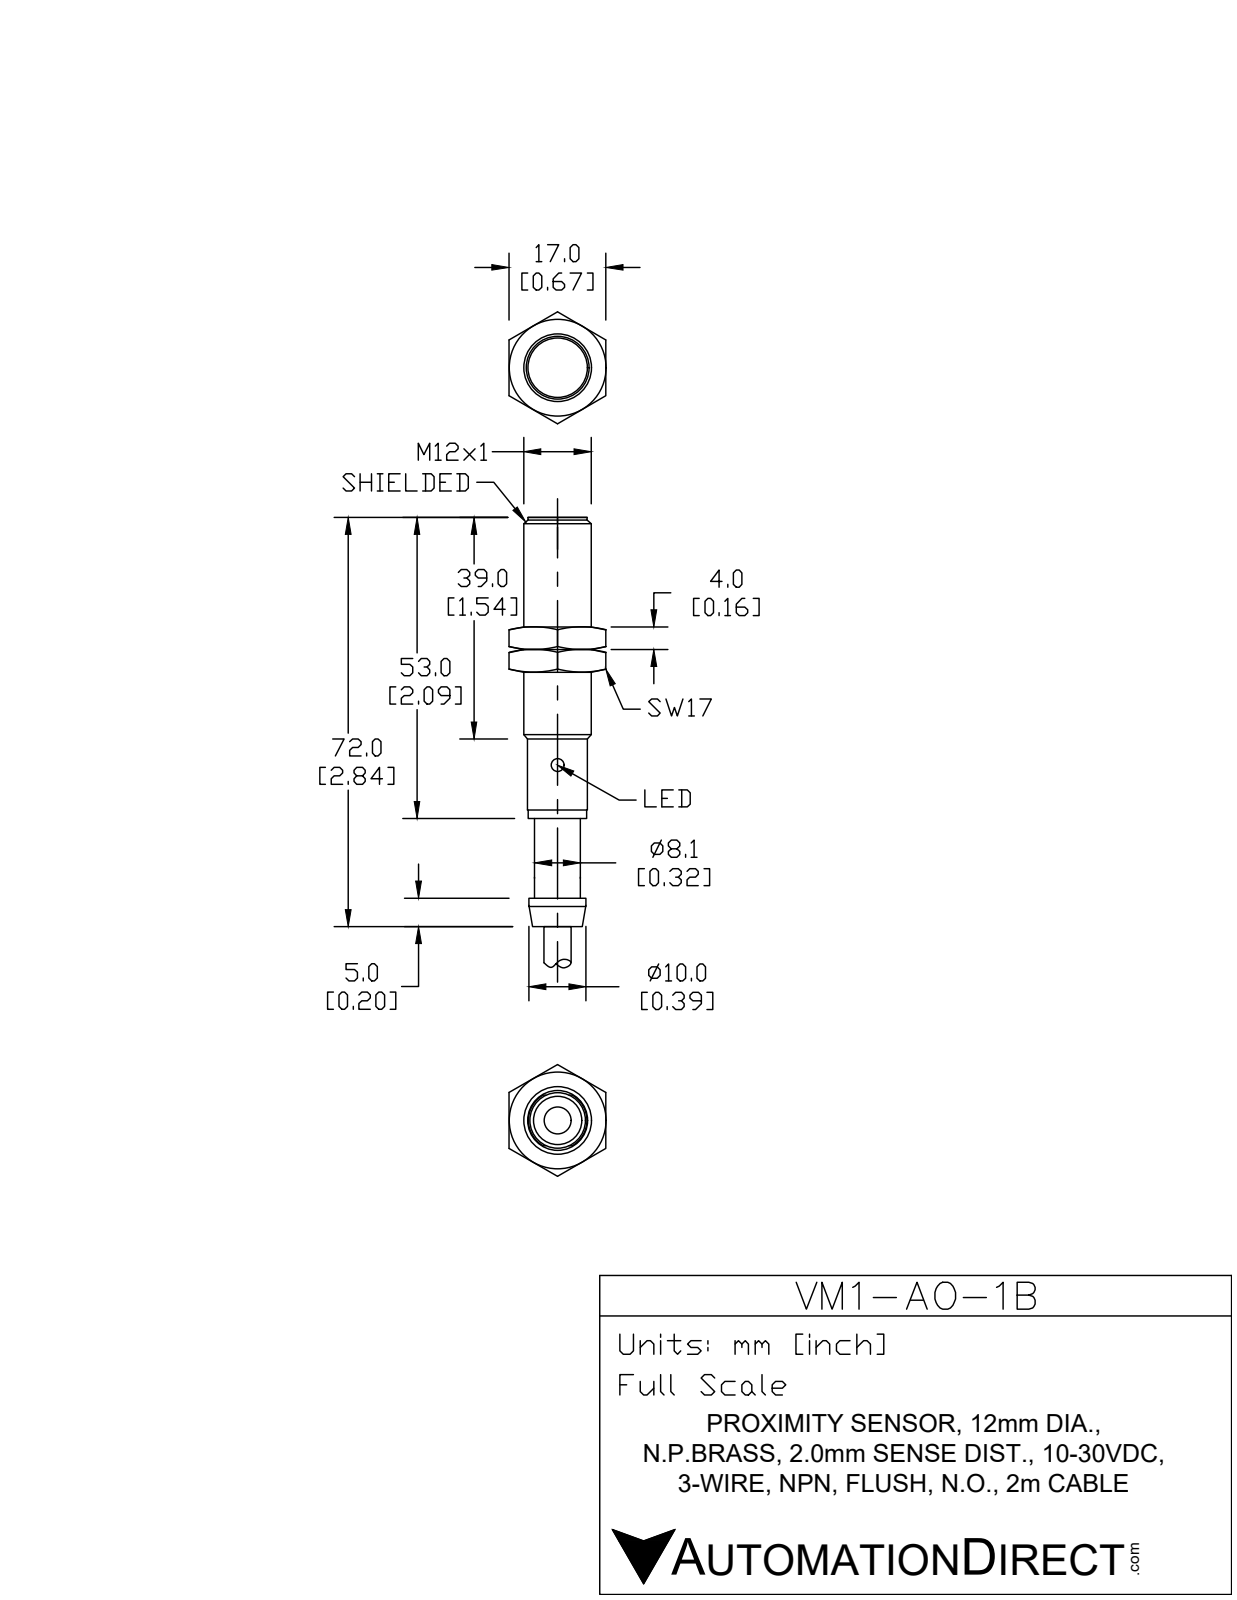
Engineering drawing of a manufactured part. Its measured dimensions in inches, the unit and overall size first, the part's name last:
Units: inches
Overall size (bounding box): 3.681 × 0.472 × 0.472
Round holes (diameter × count): ⌀0.098 ×1, ⌀0.193 ×1
Round bosses / shafts (diameter × count): ⌀0.472 ×1, ⌀0.413 ×1, ⌀0.406 ×1, ⌀0.315 ×1, ⌀0.185 ×1
Main face-to-face distances: 2.087, 0.02, 2.106, 2.165, 2.146, 0.059, 2.835, 2.815, 0.728, 0.669
Volume: 0.433 in³ · Surface area: 6.093 in²
Bodies: 4 solids, 39 faces (11 planar, 16 cylindrical, 12 other)
Part name (STEP PRODUCT): VM1-A0-1B
STEP written by: SolidWorks 2017 (AUTOMOTIVE_DESIGN)
